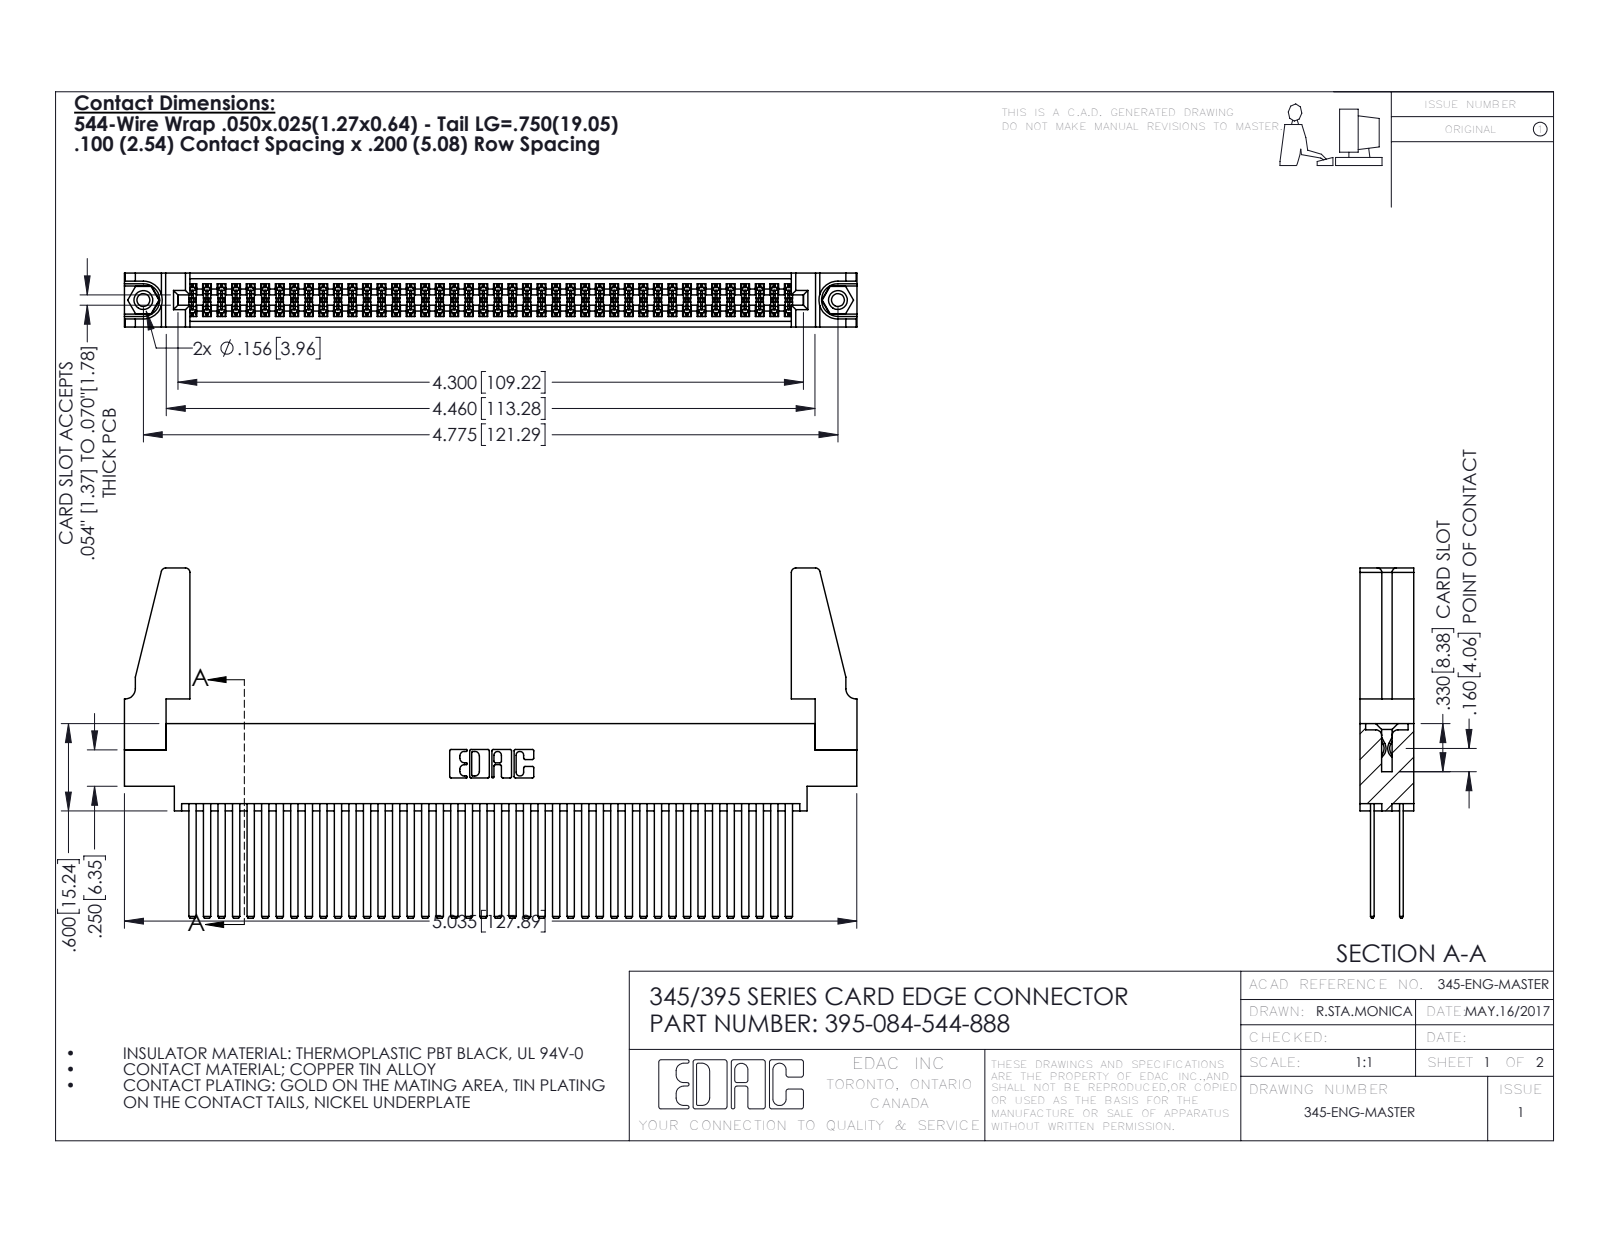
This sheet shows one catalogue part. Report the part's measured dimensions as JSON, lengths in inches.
{"part_name": "345-292-001_345-293-144; 345-220-078_345-220-088; 395-084-544-888; 345-250-001_345-250-001-102 (+1 more)", "step_written_by": "SolidWorks 2016 (CONFIG_CONTROL_DESIGN)", "units": "inches", "bodies": {"solids": 89, "faces": 3950, "planar": 2592, "cylindrical": 1342, "other": 16}, "overall_size": [5.036, 2.407, 0.37], "volume_in3": 1.022, "surface_area_in2": 41.32, "round_holes": [[0.089, 2], [0.125, 2], [0.156, 2], [0.064, 1]], "round_bosses_or_shafts": [[0.155, 2]], "partial_cylinders_radius": [[0.006, 126], [0.01, 22], [0.03, 8], [0.007, 6], [0.031, 6], [0.026, 3], [0.014, 2], [0.019, 2]], "face_to_face_distances": [0.072, 0.298, 0.2, 0.098, 0.272, 0.025, 0.37, 0.225, 0.175, 0.149], "hole_center_spacings": [0.27, 4.539, 4.775]}
